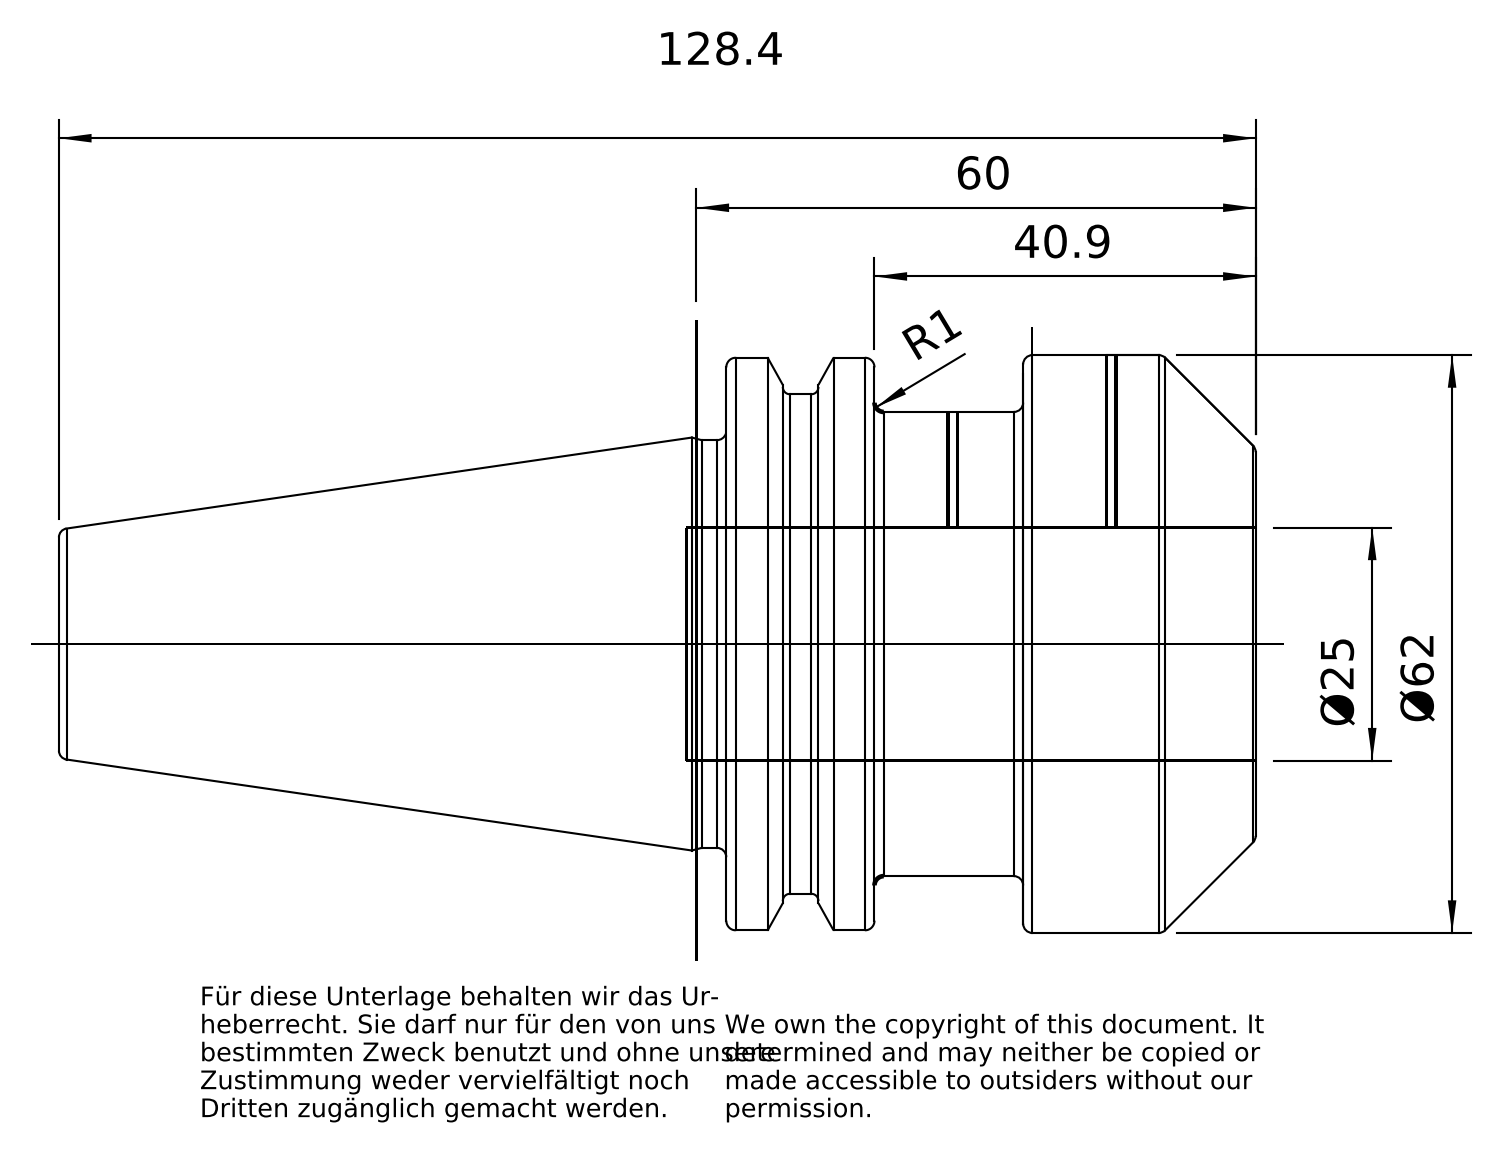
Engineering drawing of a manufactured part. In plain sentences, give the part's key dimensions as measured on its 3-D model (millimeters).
The part is named "40-305-25". Its 3-D file was written by "PRO/ENGINEER BY PARAMETRIC TECHNOLOGY CORPORATION, 2010430 (CONFIG_CONTROL_DESIGN)". It is 1 solid with 106 faces: 25 planar, 30 cylindrical and 51 other. Overall it measures 128.25 by 63.52 by 62 millimeters. Its volume is 170 254 cubic millimeters and its surface area 34 144 square millimeters. Round holes: 1 of diameter 13.84, 1 of diameter 16, 1 of diameter 17.01, 1 of diameter 17.5, 1 of diameter 18, 1 of diameter 25. Round bosses or shafts: 1 of diameter 62, 1 of diameter 49.8, 1 of diameter 43.75, 1 of diameter 16.01. Partial cylindrical surfaces (rounded edges, fillets, slot ends): 1 of radius 1.35, 1 of radius 28, 1 of radius 31.76. The main face-to-face distances are 56.8, 15.85, 40.95, 31.85, 16, 24.95, 4.3, 20.15, 36.15, 61.1.
